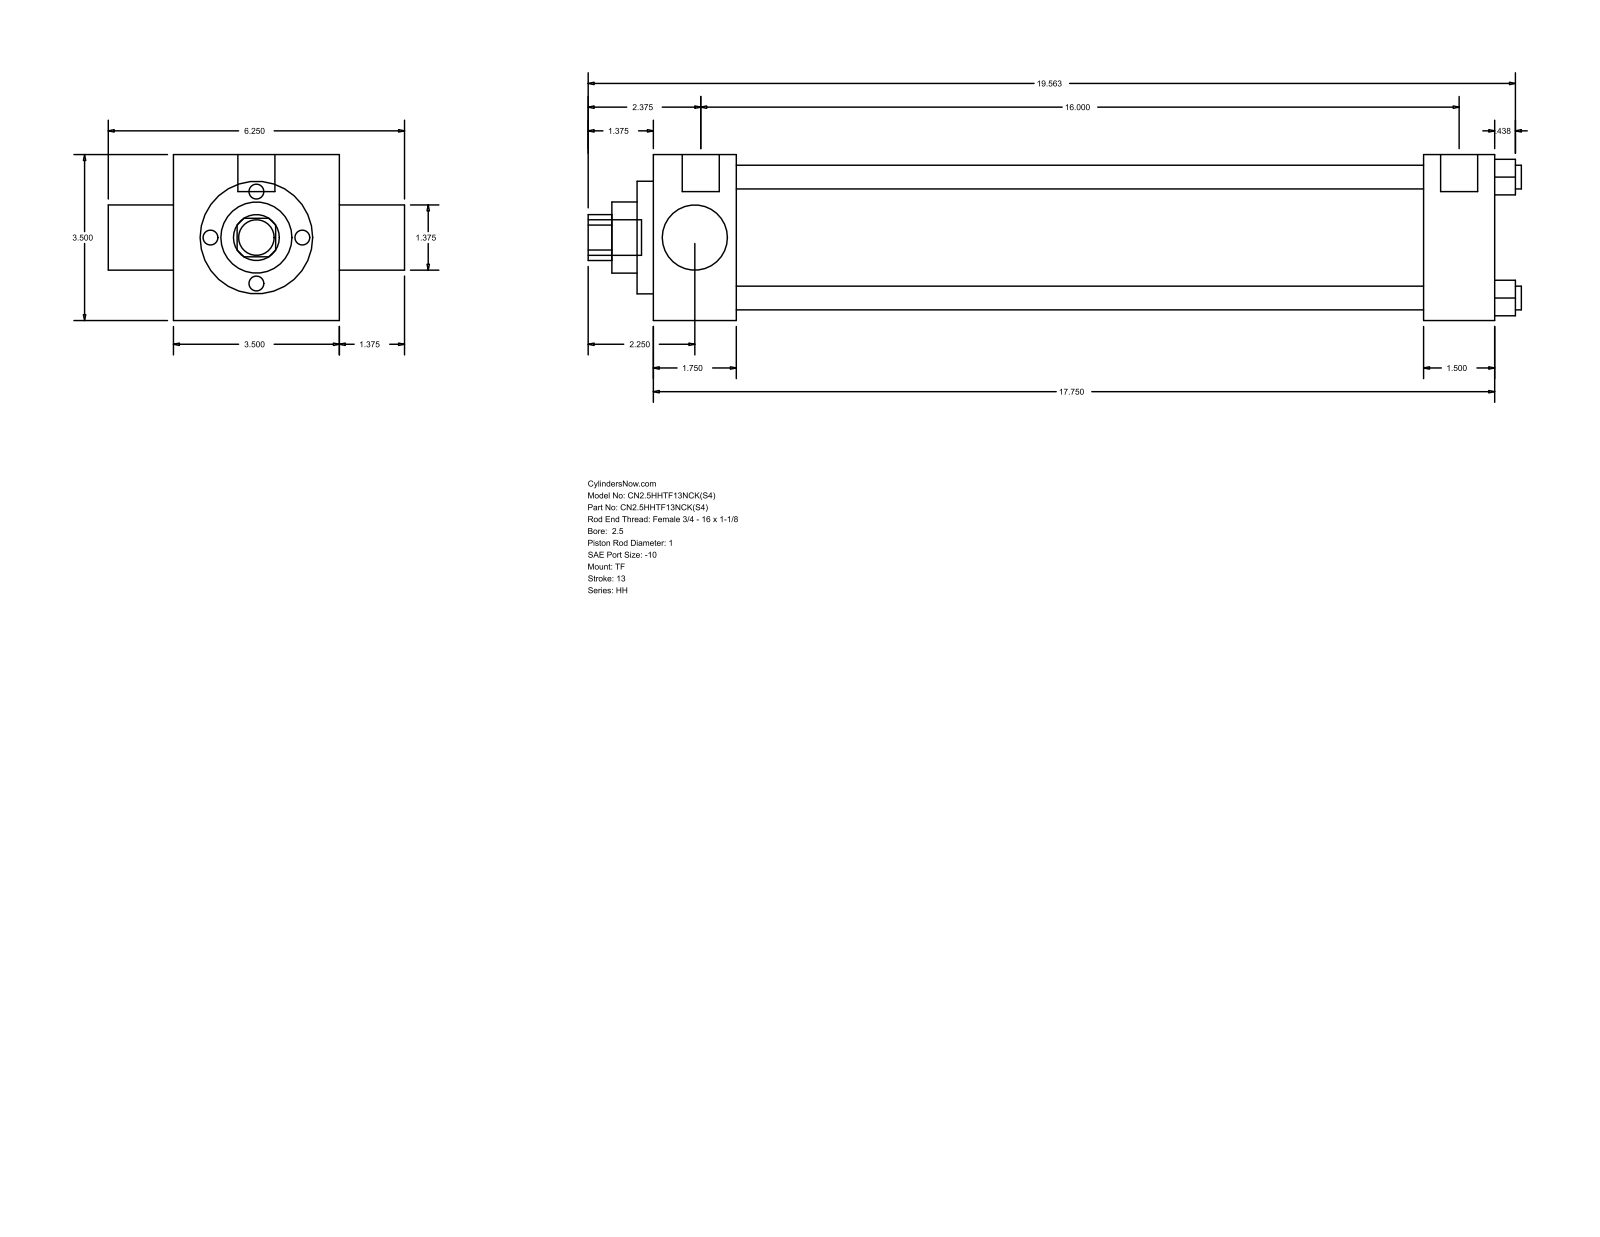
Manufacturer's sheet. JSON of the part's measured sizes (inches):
{"part_name": "HH_TF__0250_1", "step_written_by": "GSSL Pune (CONFIG_CONTROL_DESIGN)", "units": "inches", "bodies": {"solids": 0, "faces": 86, "planar": 61, "cylindrical": 25, "other": 0}, "overall_size": [19.687, 6.25, 3.5], "round_holes": [[0.5, 4], [1, 1], [1.375, 1], [1.5, 1], [2.375, 1], [2.875, 1]], "round_bosses_or_shafts": [[0.219, 3], [0.781, 2], [0.75, 1]], "partial_cylinders_radius": [[0.484, 1]], "face_to_face_distances": [3.5, 17.75, 1.75, 16, 16.25, 14.5, 1.5, 1.375, 4.875, 0.344], "hole_center_spacings": [1.803, 2.55, 3.606]}
